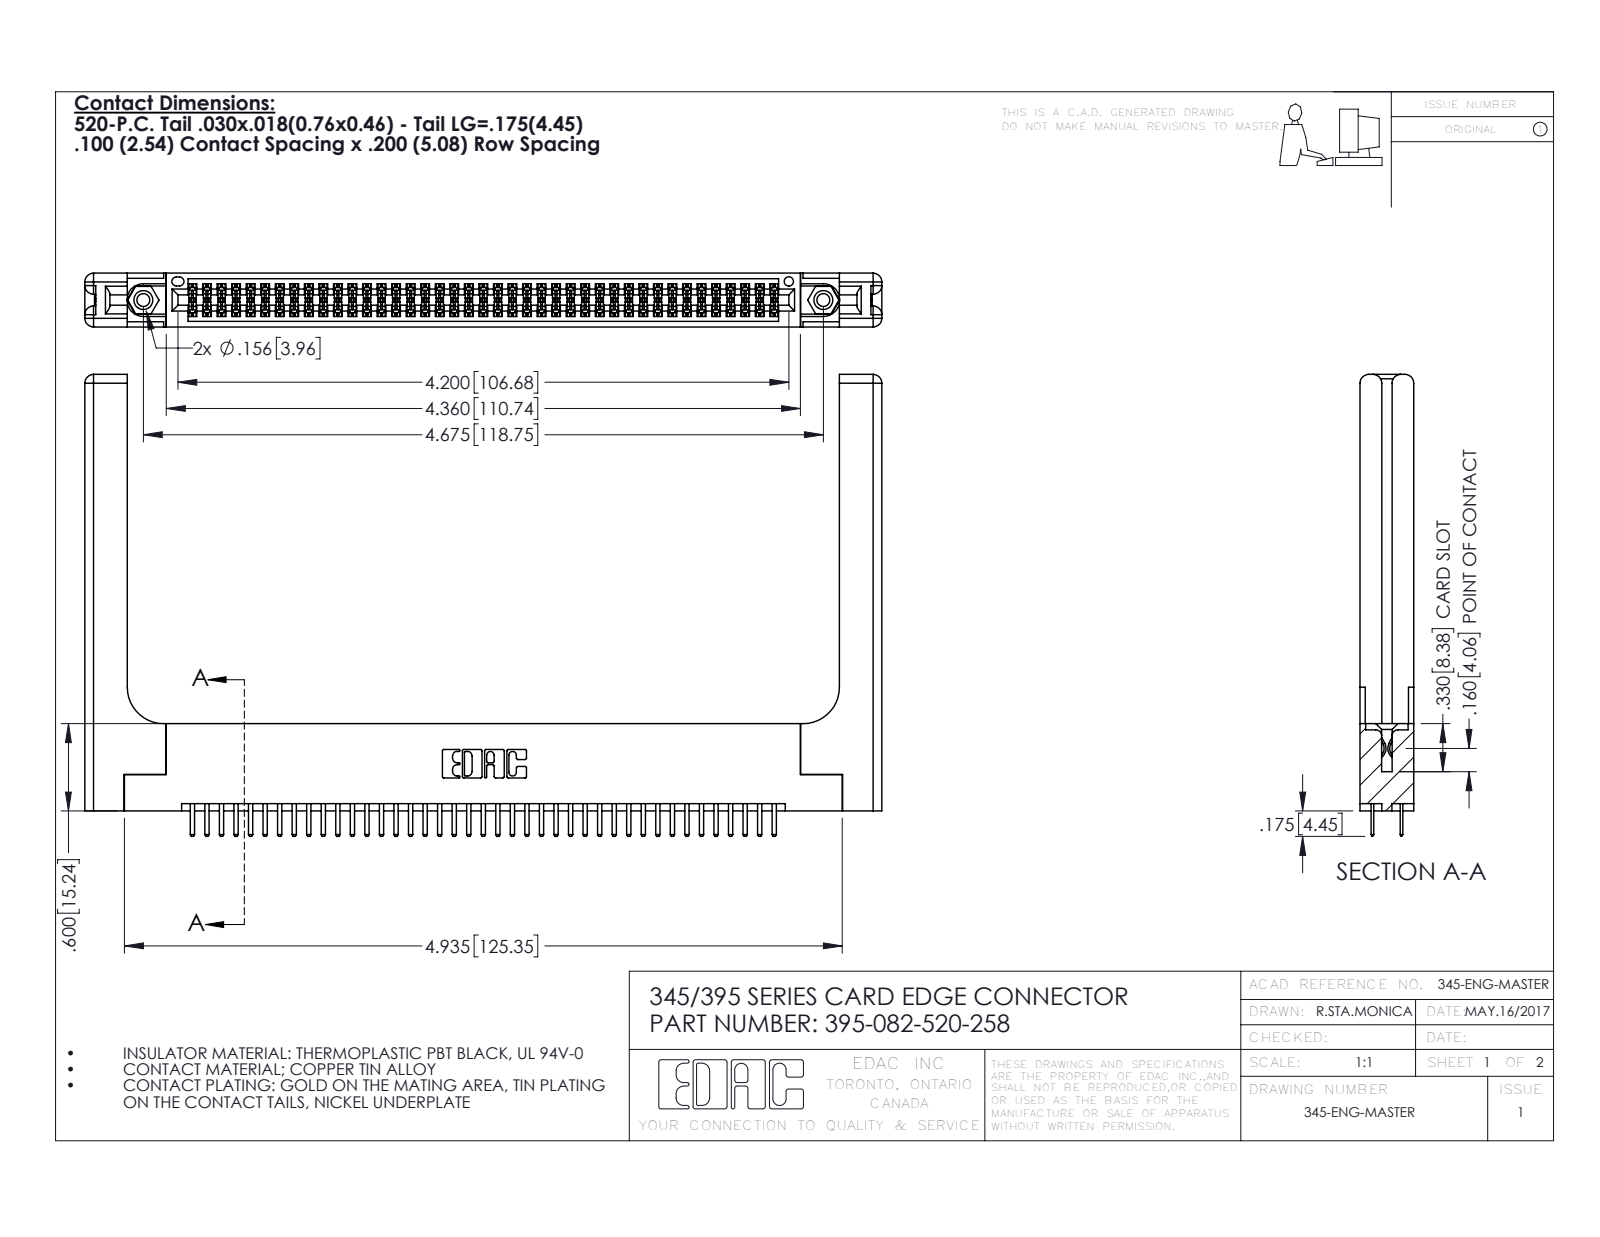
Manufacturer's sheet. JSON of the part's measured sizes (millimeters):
{"part_name": "395-082-520-258; 345 Part_Flush Mounting Lugs - 0.156 Dia-TH; 345-220-058_345-220-058; 345-292-001_345-293-120 (+1 more)", "step_written_by": "SolidWorks 2016 (CONFIG_CONTROL_DESIGN)", "units": "millimeters", "bodies": {"solids": 87, "faces": 4810, "planar": 3098, "cylindrical": 1652, "other": 60}, "overall_size": [139.2, 80.6, 9.4], "volume_mm3": 21940, "surface_area_mm2": 24880, "round_holes": [[2.3, 2], [3.2, 2], [4, 2], [1.6, 1]], "round_bosses_or_shafts": [[3.9, 2]], "partial_cylinders_radius": [[0.2, 123], [0.3, 86], [0.3, 22], [1.5, 16], [0.2, 6], [0.8, 6], [0.7, 3], [0.4, 2]], "face_to_face_distances": [9.4, 1.8, 7.6, 5.1, 2.5, 6.9, 0.6, 5.7, 3.8, 3.8], "hole_center_spacings": [6.9, 112.8, 118.7]}
